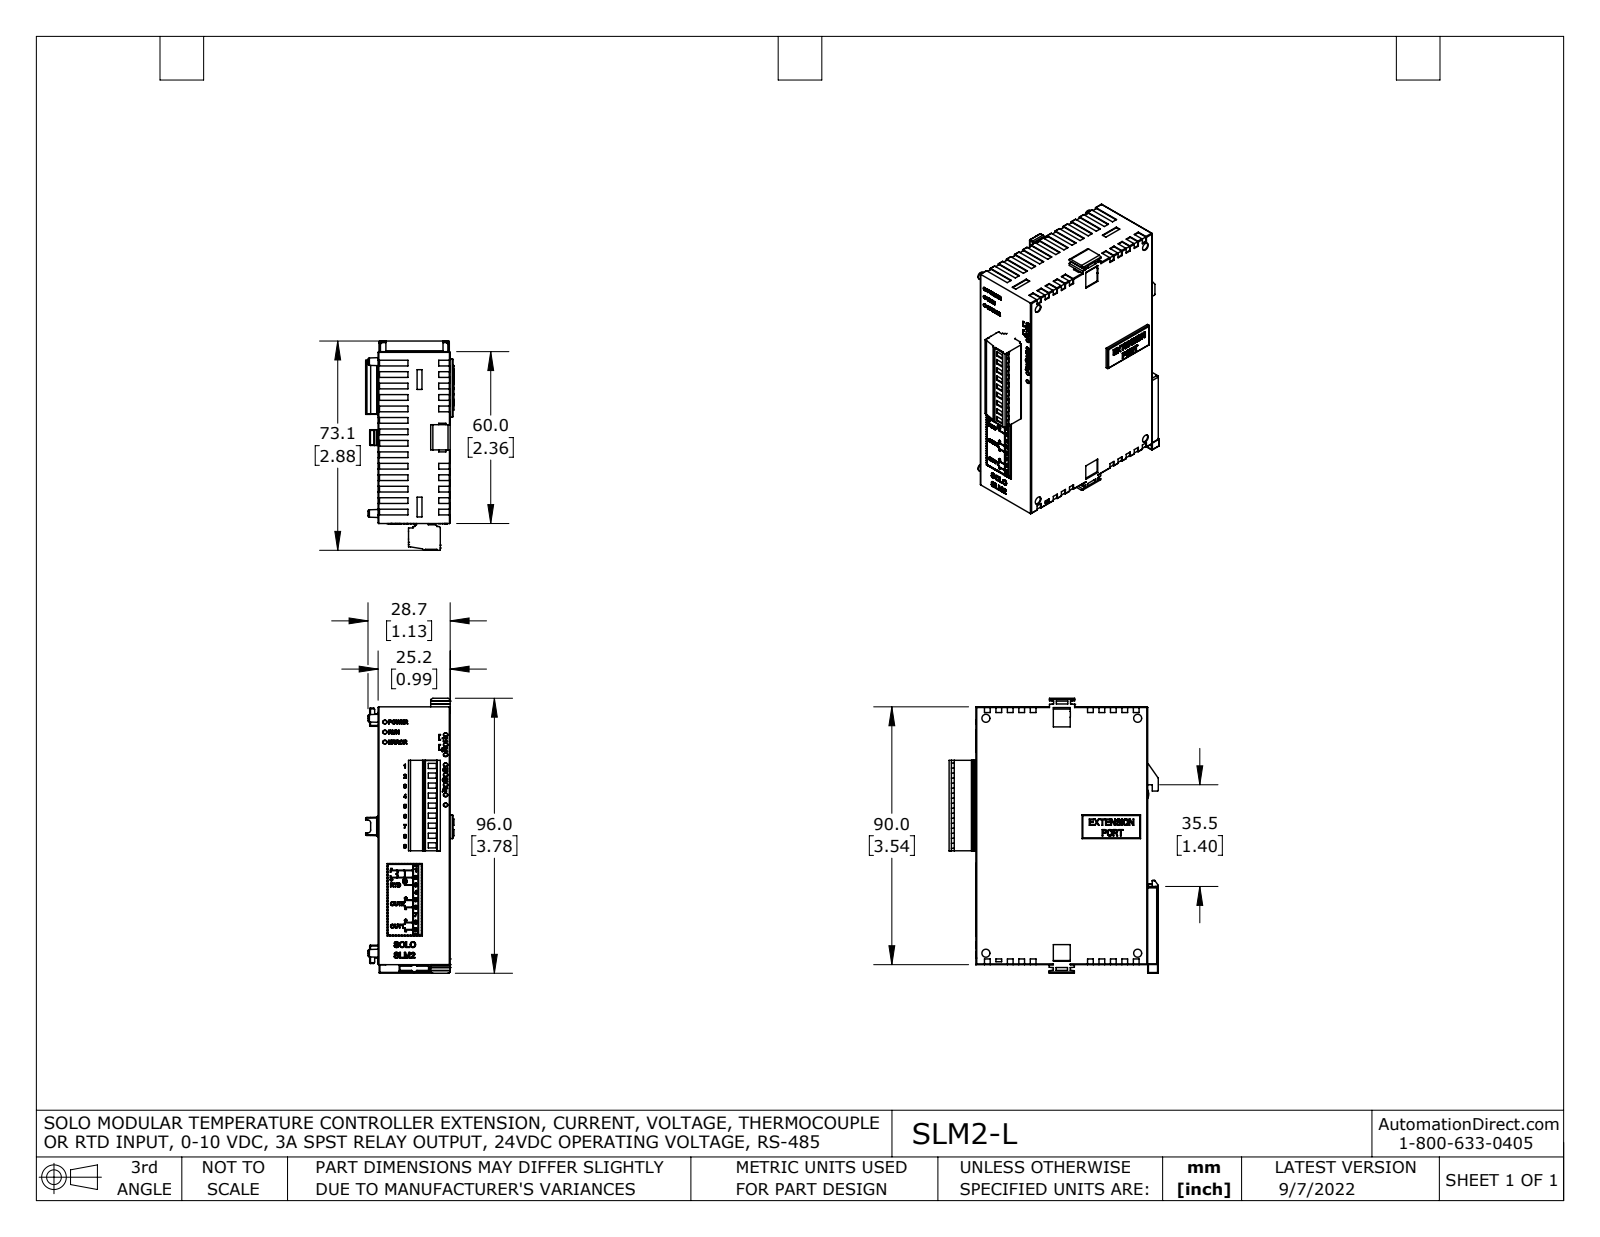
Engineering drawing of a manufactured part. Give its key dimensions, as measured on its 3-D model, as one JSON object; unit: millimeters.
{"part_name": "SLM2-C sr1 fxt sra coord", "step_written_by": "SolidWorks 2021 (AUTOMOTIVE_DESIGN)", "units": "millimeters", "bodies": {"solids": 4, "faces": 3638, "planar": 2408, "cylindrical": 334, "other": 896}, "overall_size": [96, 73.1, 30.8], "volume_mm3": 140600, "surface_area_mm2": 28490, "round_holes": [[2.7, 9], [2.8, 4], [2.4, 2]], "partial_cylinders_radius": [[0.3, 63], [0.6, 24], [0.6, 22], [0.5, 11], [1.5, 9], [2.3, 9], [0.3, 6], [0.5, 6]], "face_to_face_distances": [25.2, 59.7, 0.5, 24.7, 60, 90, 89.7, 2, 3.7, 63.7], "hole_center_spacings": [6.9, 13.7, 3.4, 3.5, 26.5, 85.4, 10.2, 10.3]}
